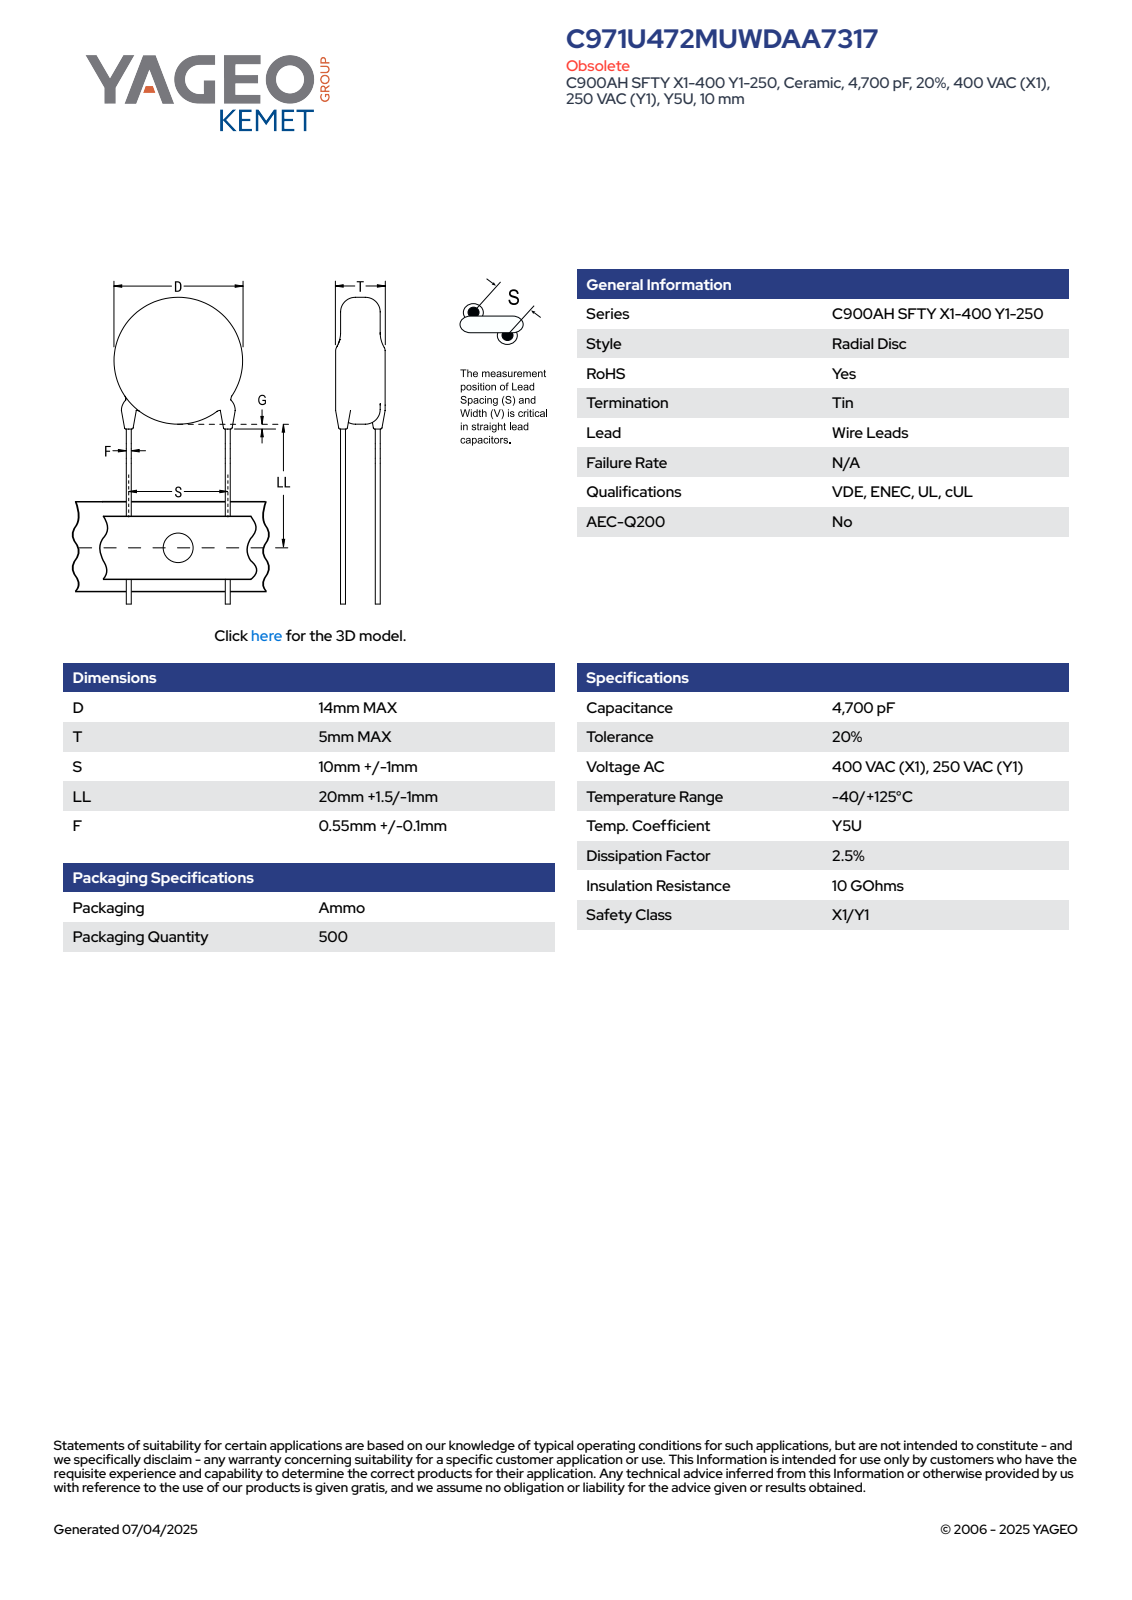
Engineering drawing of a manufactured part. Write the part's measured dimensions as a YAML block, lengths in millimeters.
part_name: "CCD_STC900_D14T5S10LL21.5F0.65G3"
step_written_by: "SolidWorks 2014 (AUTOMOTIVE_DESIGN)"
units: millimeters
bodies: {solids: 4, faces: 83, planar: 61, cylindrical: 6, other: 16}
overall_size: [35.5, 14, 5]
volume: 768
surface_area: 601
round_bosses_or_shafts:
  - {diameter: 0.65, count: 2}
  - {diameter: 14, count: 1}
face_to_face_distances: [5, 29.3, 27.69, 1.61, 0.4, 6.61, 0.44, 0.6, 0.31, 1.3]
